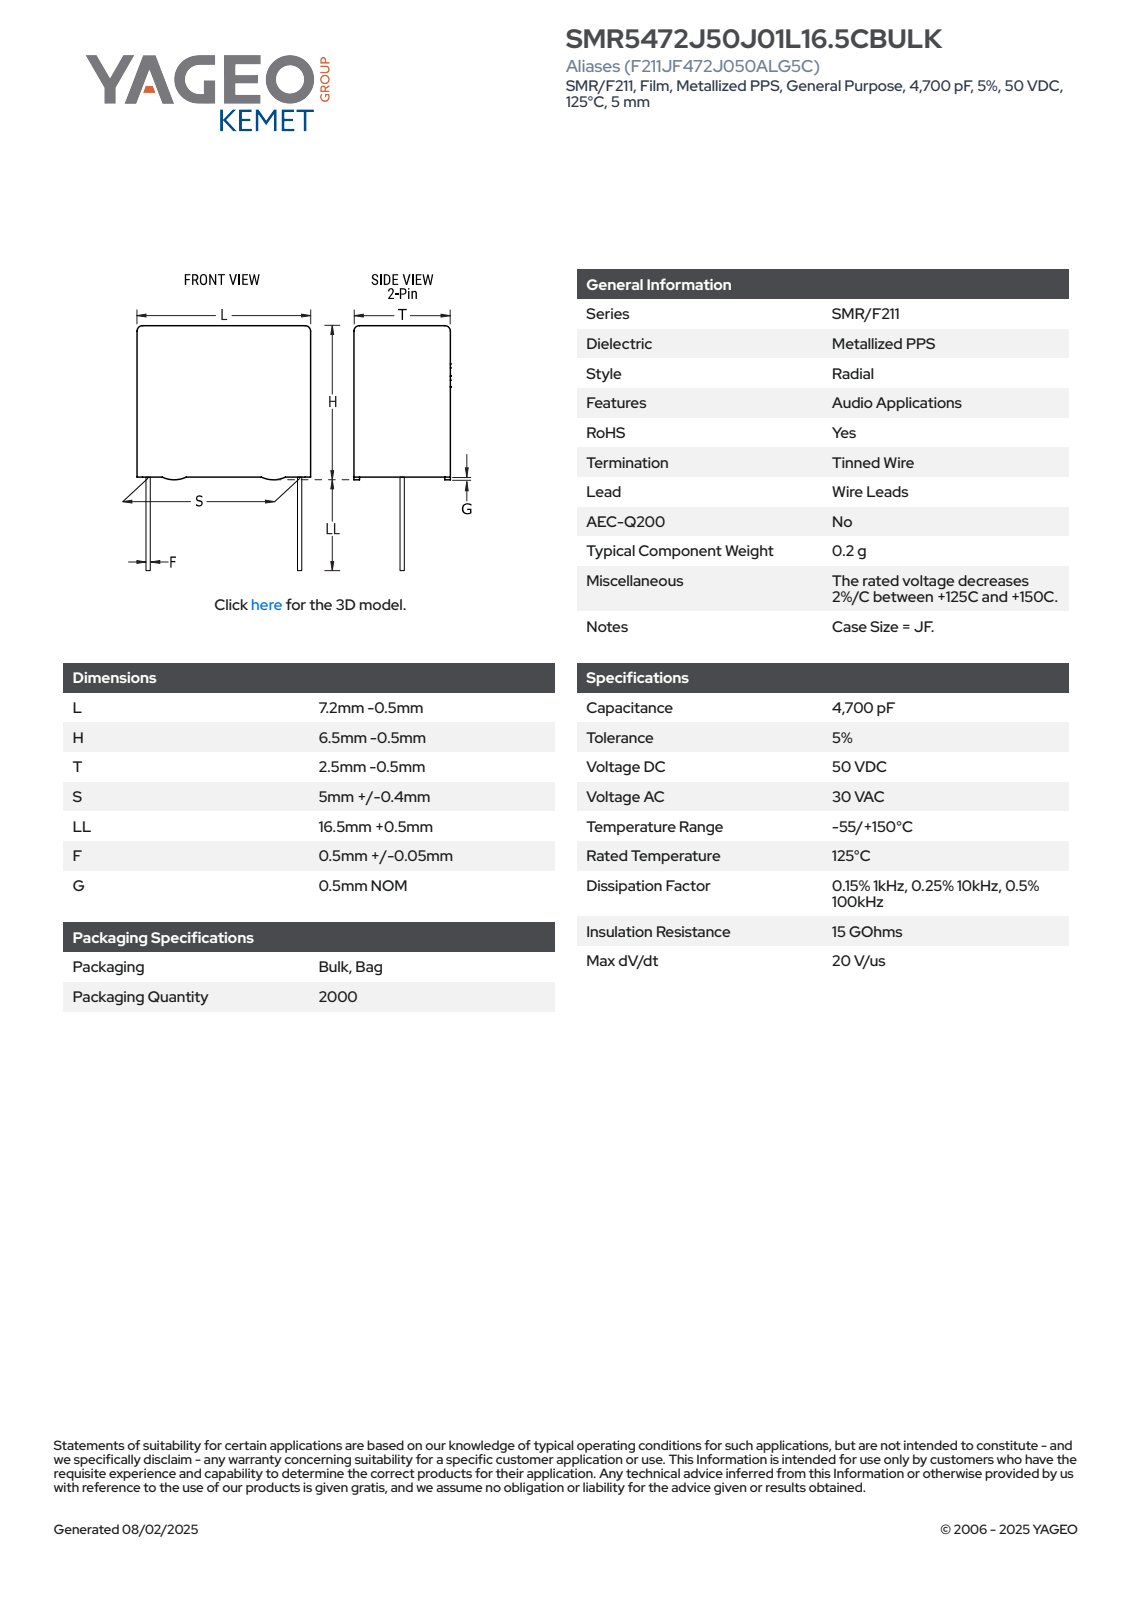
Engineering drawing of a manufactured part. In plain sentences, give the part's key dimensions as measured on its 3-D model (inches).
The part is named "CFR_RBG_7.2X6.5X2.5_L6.7H6T2S5LL17F0.55G0.5". Its 3-D file was written by "SolidWorks 2021 (AUTOMOTIVE_DESIGN)". It is 4 solids with 89 faces: 81 planar, 8 cylindrical and 0 other. Overall it measures 0.906 by 0.264 by 0.079 inches. Its volume is 0.005 cubic inches and its surface area 0.293 square inches. Round bosses or shafts: 2 of diameter 0.022. Partial cylindrical surfaces (rounded edges, fillets, slot ends): 4 of radius 0.02. The main face-to-face distances are 0.079, 0.264, 0.217, 0.074, 0.07, 0.689, 0.906, 0.669, 0.02, 0.236.
